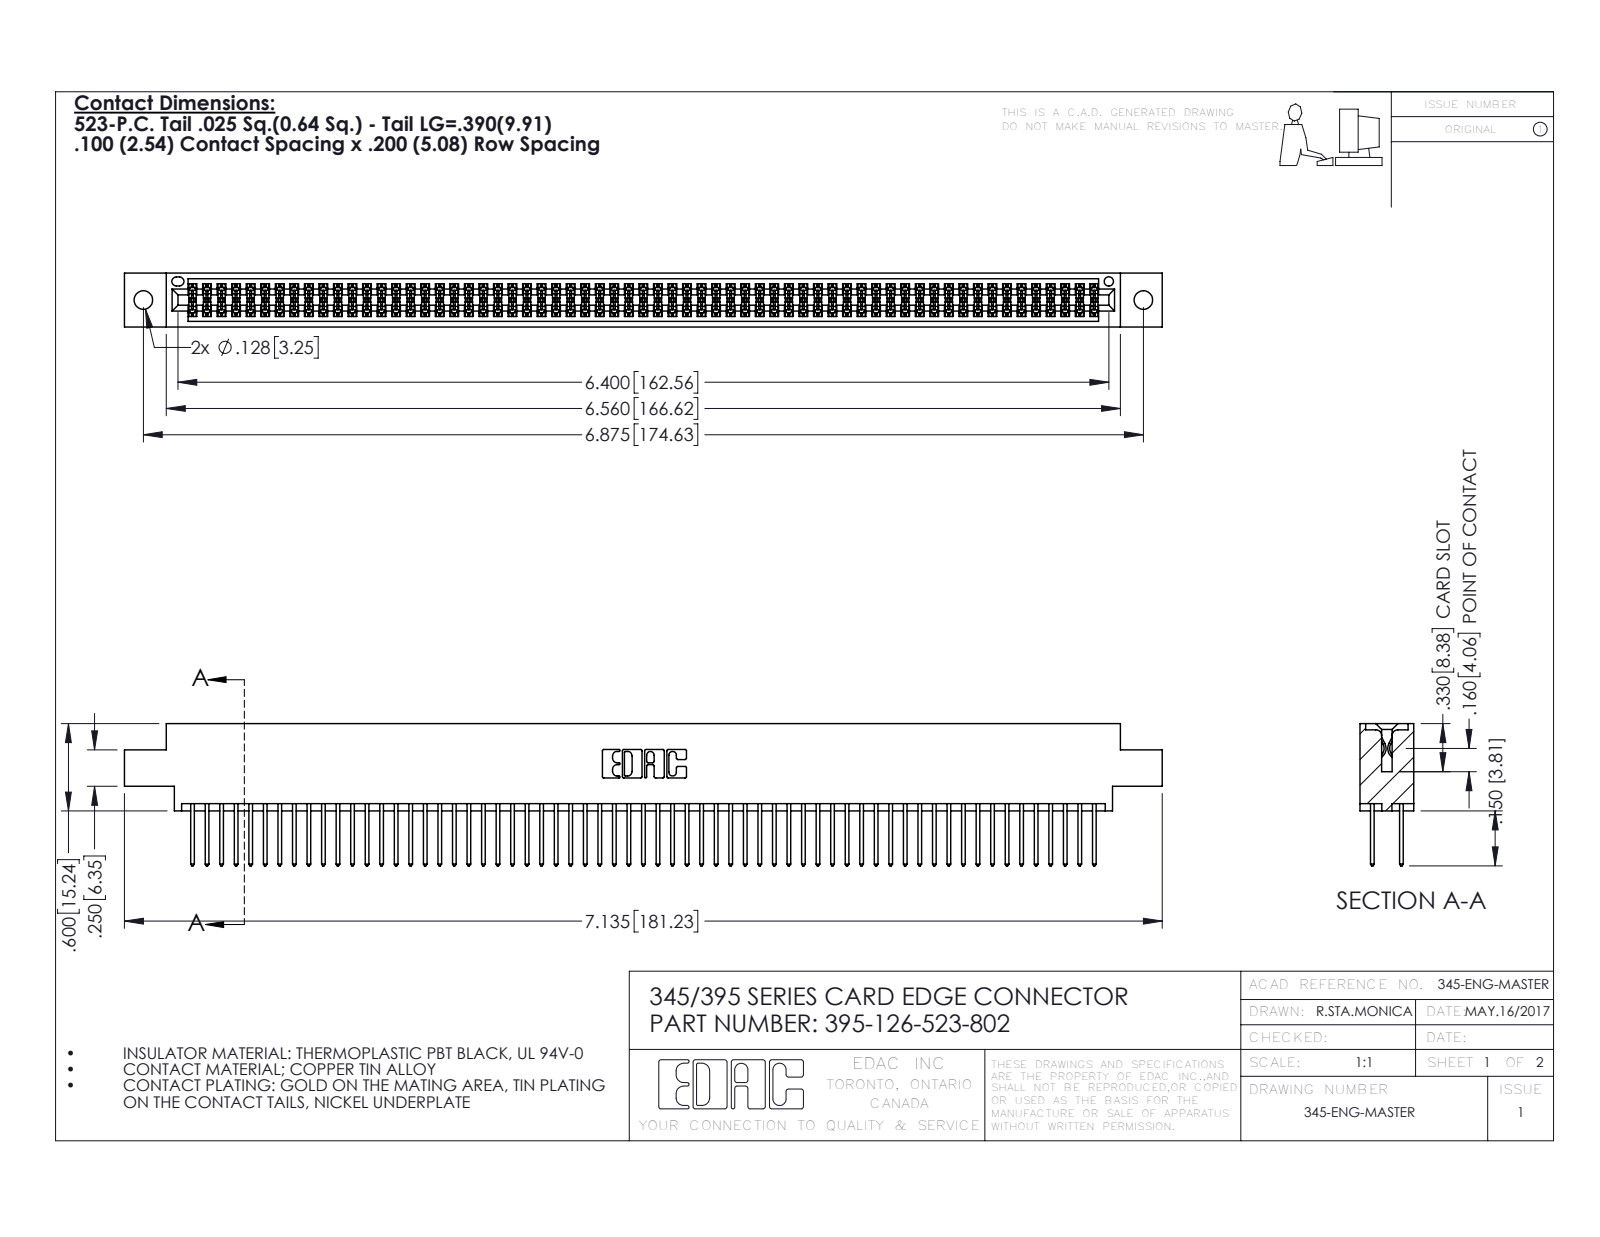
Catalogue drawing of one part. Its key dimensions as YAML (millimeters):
part_name: "345-292-001_345-293-123; 345 Part_0.170 Offset - 0.128 Dia; 395-126-523-802"
step_written_by: "SolidWorks 2016 (CONFIG_CONTROL_DESIGN)"
units: millimeters
bodies: {solids: 127, faces: 6430, planar: 4242, cylindrical: 2188, other: 0}
overall_size: [181.2, 24.8, 9.4]
volume: 17910
surface_area: 27910
round_holes:
  - {diameter: 3.3, count: 2}
  - {diameter: 1.6, count: 1}
partial_cylinders:
  - {radius: 0.2, count: 189}
  - {radius: 0.3, count: 126}
  - {radius: 0.3, count: 22}
  - {radius: 0.2, count: 6}
  - {radius: 0.8, count: 6}
  - {radius: 0.7, count: 3}
  - {radius: 0.4, count: 2}
  - {radius: 0.5, count: 2}
face_to_face_distances: [7.6, 1.8, 5.1, 2.5, 6.9, 0.6, 9.4, 5.7, 4.4, 3.8]
hole_center_spacings: [6.9, 168.6, 174.6]
